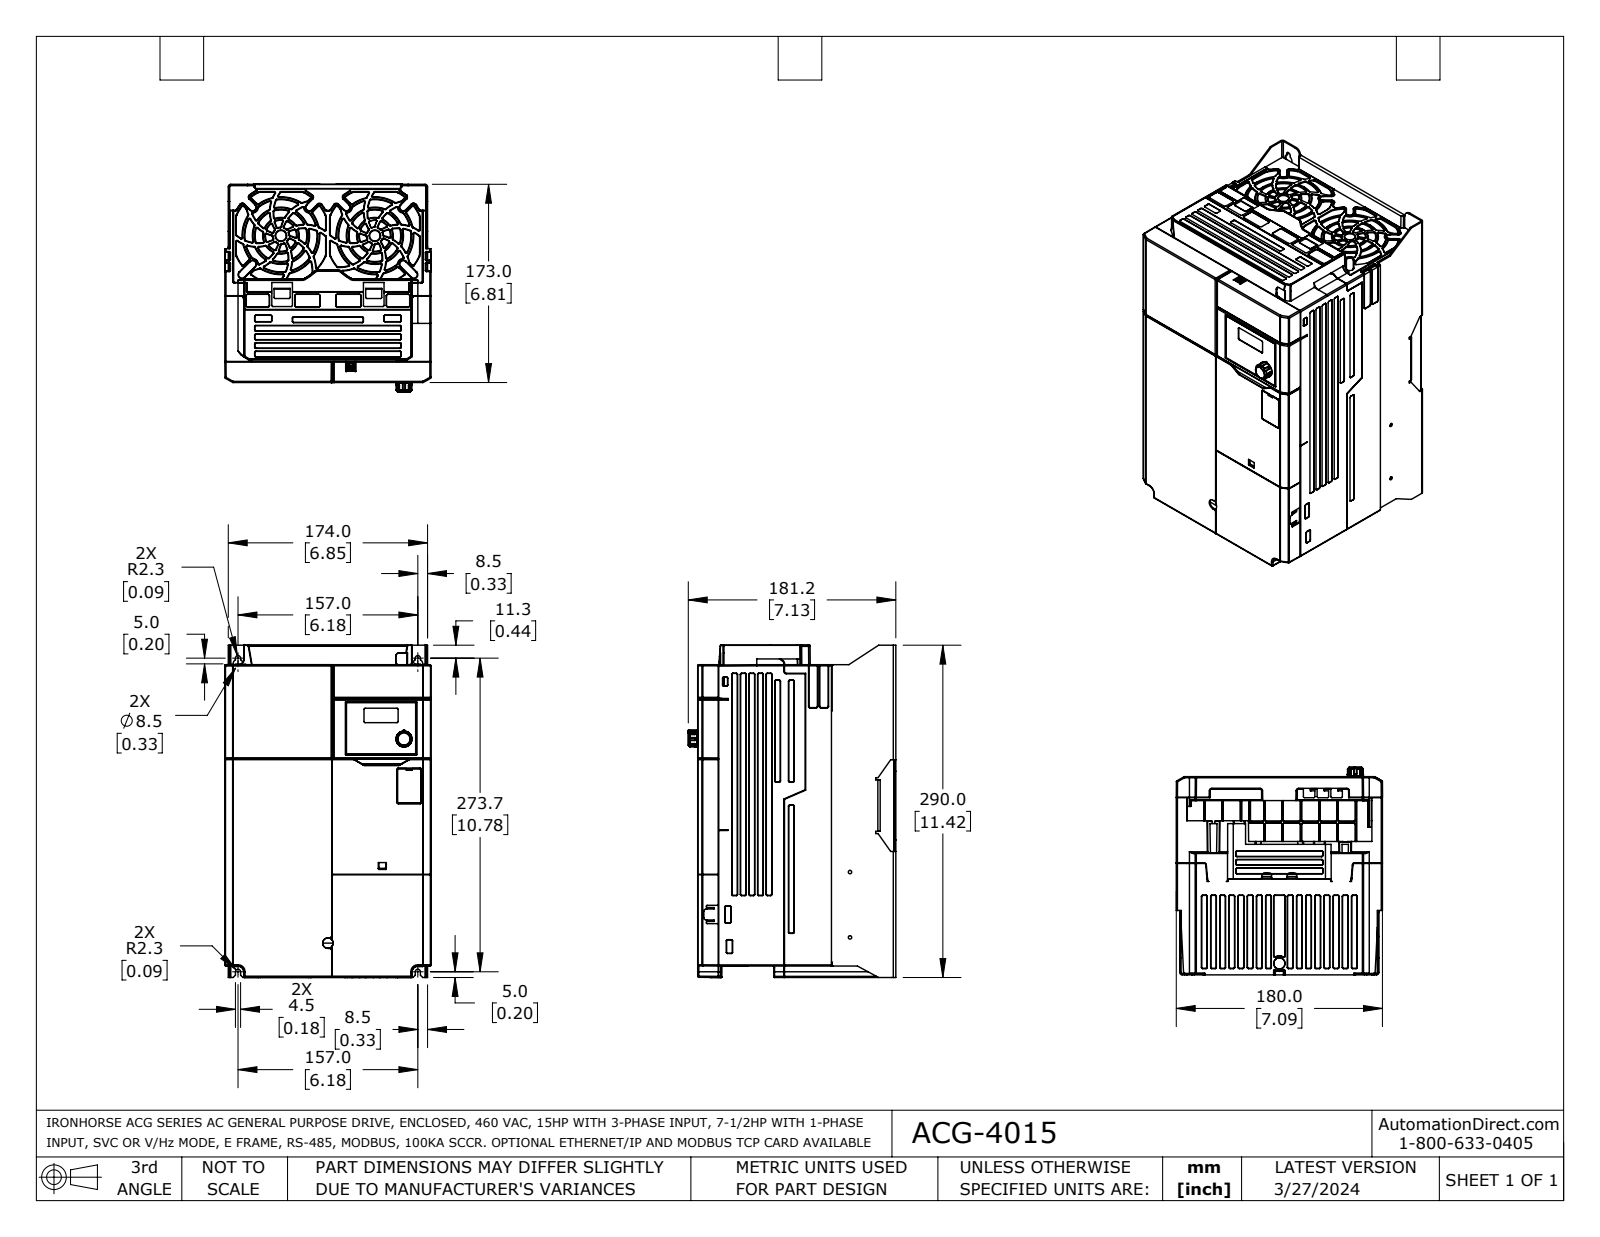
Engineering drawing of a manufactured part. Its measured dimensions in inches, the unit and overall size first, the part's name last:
Units: inches
Overall size (bounding box): 11.418 × 7.134 × 7.087
Round holes (diameter × count): ⌀0.161 ×4, ⌀0.177 ×3, ⌀0.217 ×3, ⌀0.118 ×2, ⌀0.335 ×2, ⌀0.039 ×1, ⌀0.362 ×1, ⌀0.472 ×1
Round bosses / shafts (diameter × count): ⌀0.386 ×2, ⌀0.327 ×2, ⌀0.197 ×2, ⌀0.551 ×1, ⌀0.543 ×1, ⌀0.335 ×1, ⌀0.315 ×1, ⌀0.259 ×1
Partial cylindrical surfaces — rounded edges, fillets, slot ends (radius × count): R0.039 ×124, R0.008 ×108, R0.02 ×95, R0.012 ×36, R0.079 ×14, R0.197 ×12, R0.087 ×9, R0.177 ×6
Main face-to-face distances: 0.055, 6.811, 6.756, 0.453, 6.634, 6.181, 0.118, 6.969, 0.335, 6.516
Hole centre spacings: 0.433, 0.894, 0.945, 1.378, 1.811, 1.835, 2.267, 2.7
Volume: 150.2 in³ · Surface area: 855.8 in²
Bodies: 6 solids, 3664 faces (1665 planar, 663 cylindrical, 1336 other)
Part name (STEP PRODUCT): ACG-4015
STEP written by: SolidWorks 2021 (AUTOMOTIVE_DESIGN)
